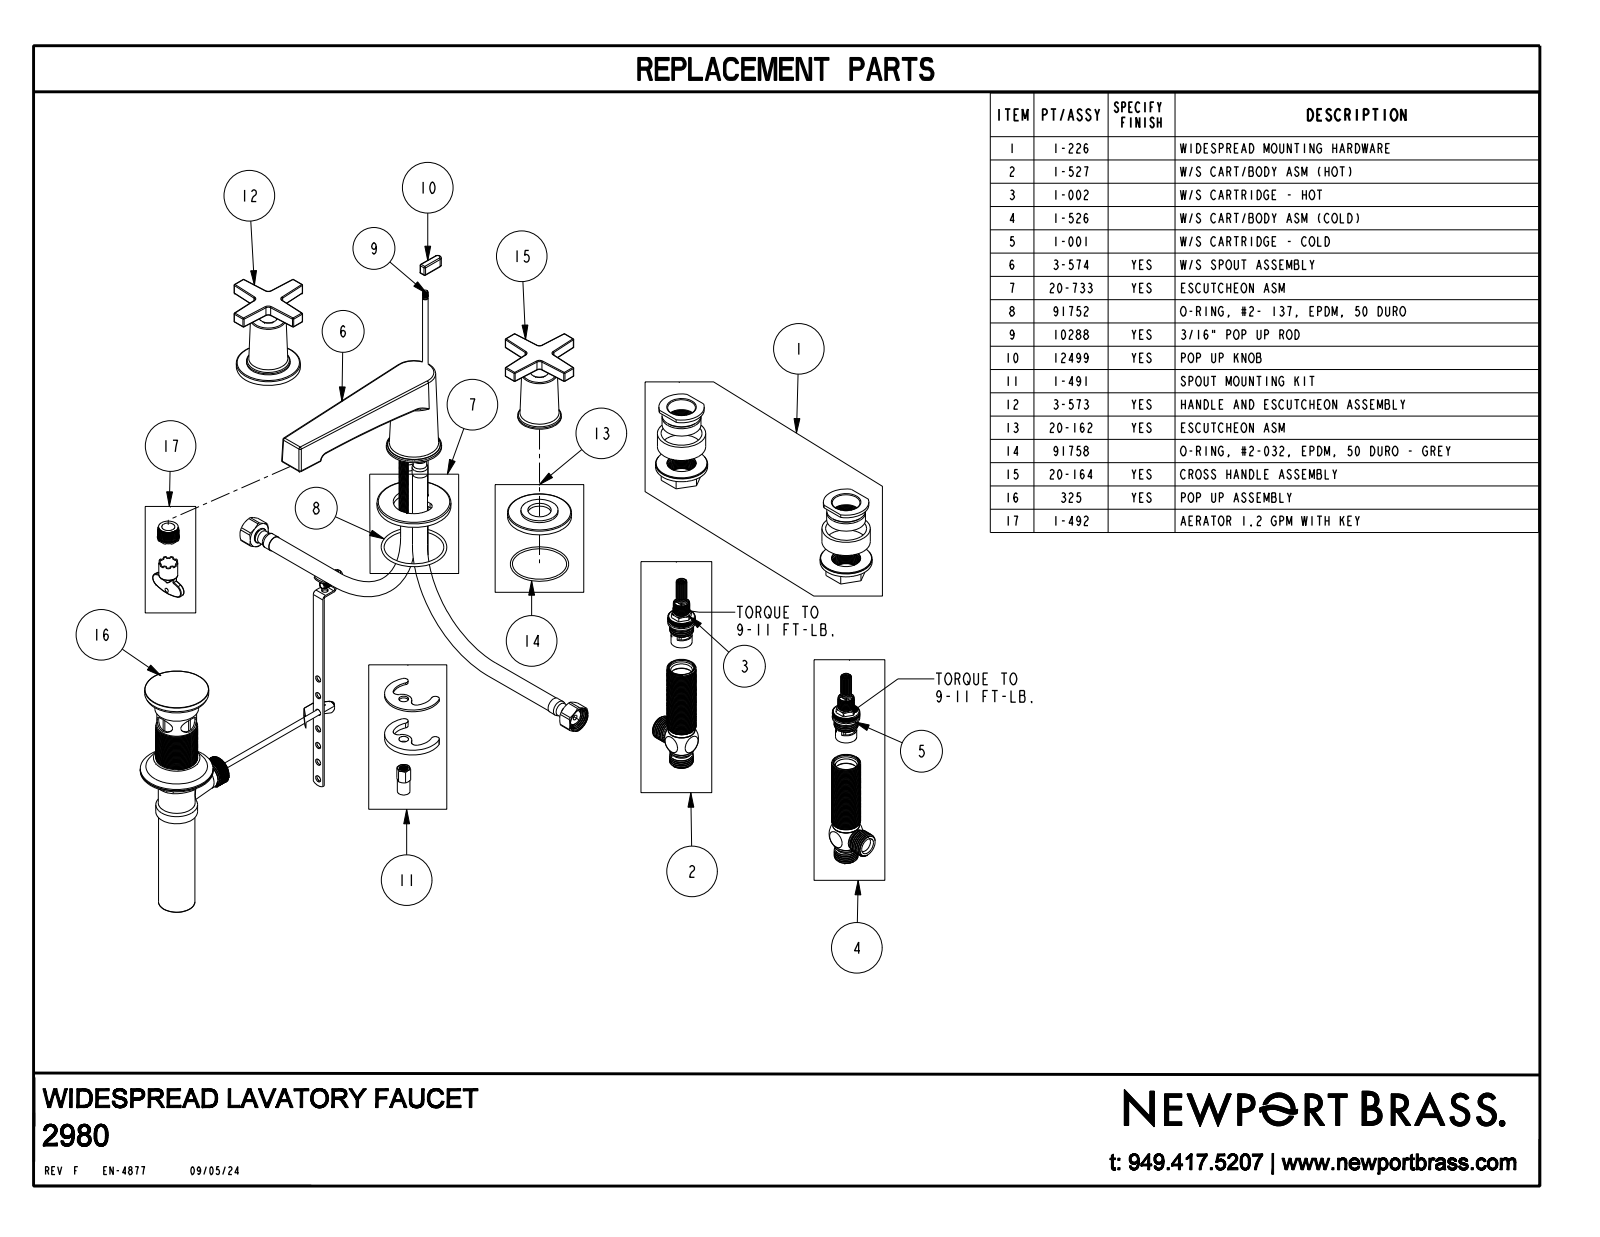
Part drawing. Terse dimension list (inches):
name: 2980
written by: CREO PARAMETRIC BY PTC INC, 2018400 (CONFIG_CONTROL_DESIGN)
unit: in
bodies: 3 solids, 276 faces (55 planar, 121 cylindrical, 100 other)
size: 10.886 × 7.441 × 3.313
volume: 20.96 in³; area: 104.9 in²
holes: 2× ⌀1.3
bosses: 2× ⌀2.2, 2× ⌀1.5, 2× ⌀1.275, 2× ⌀0.625, 2× ⌀0.525, 1× ⌀2.538
rounds: 60× R0.03, 10× R0.04, 9× R0.06, 9× R0.125, 1× R0.157, 1× R0.212, 1× R35
face distances: 3.313, 0.187, 3.126, 2.87, 2.683, 0.443, 2.495, 2.308, 0.375, 0.818
hole spacings: 8
